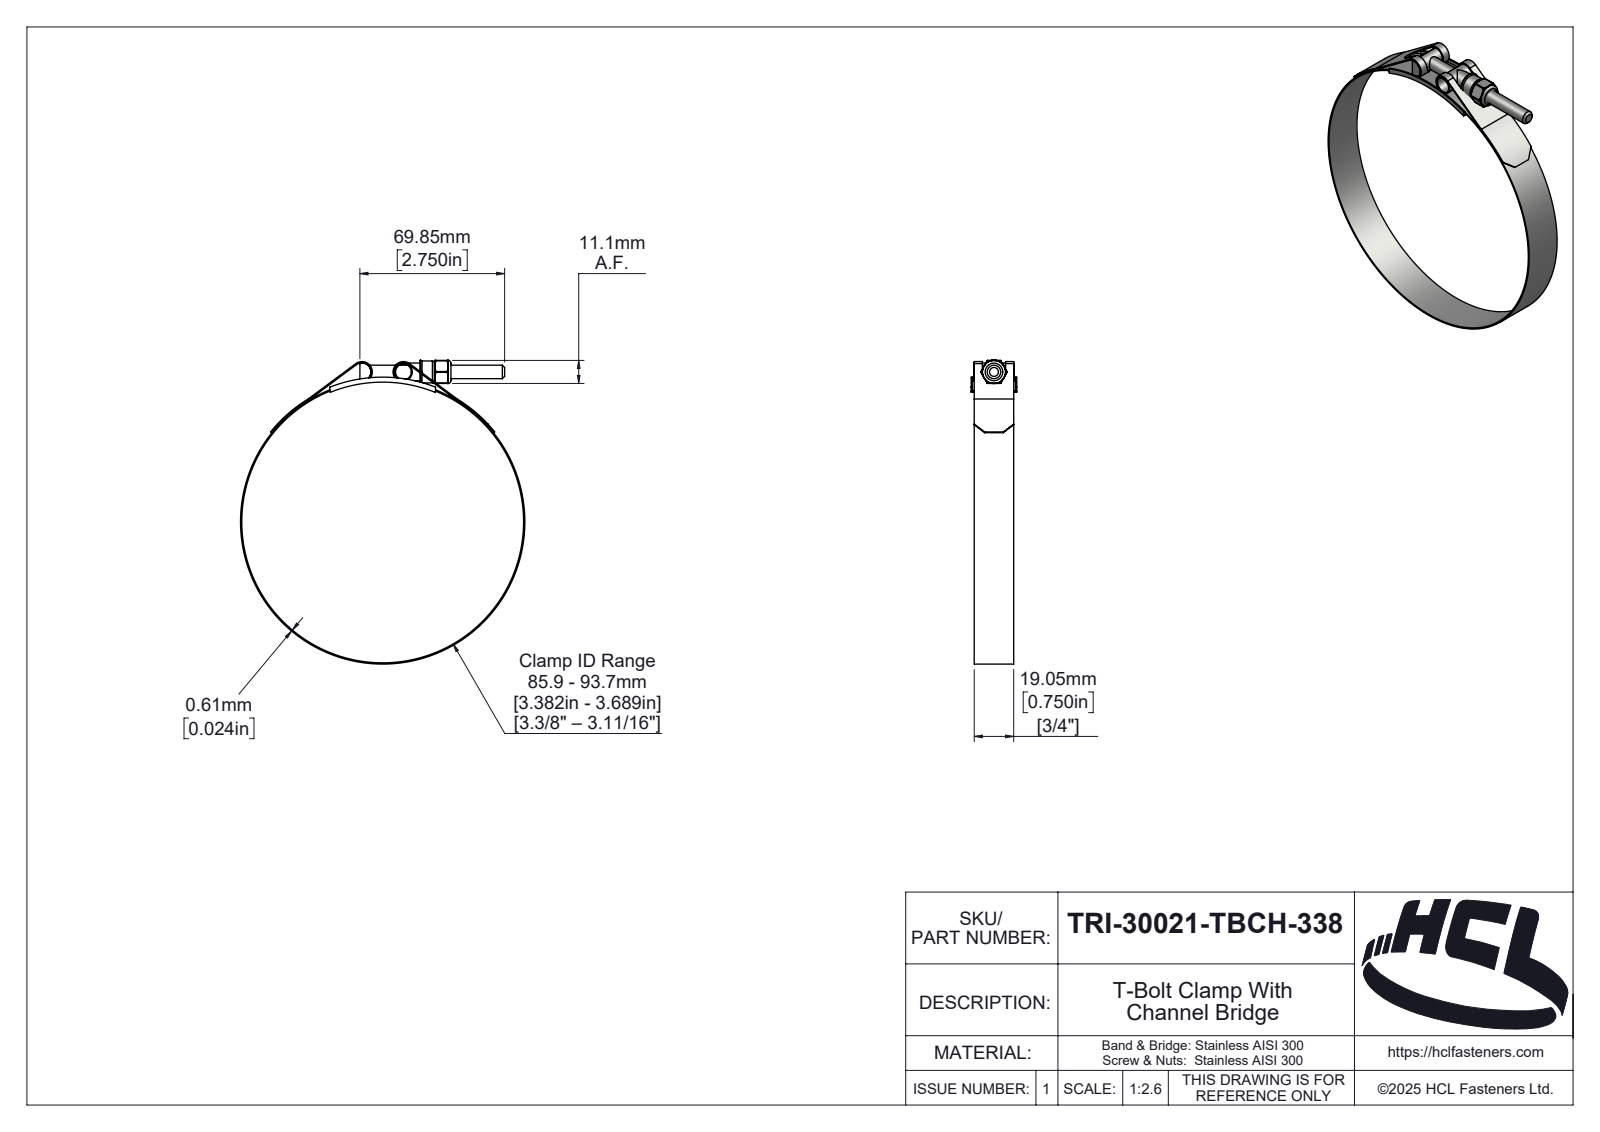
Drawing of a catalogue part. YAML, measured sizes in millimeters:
part_name: "TRI-30021-TBCH-338"
step_written_by: "SolidWorks 2025 (AUTOMOTIVE_DESIGN)"
units: millimeters
bodies: {solids: 6, faces: 330, planar: 46, cylindrical: 122, other: 162}
overall_size: [146.64, 137.22, 22]
volume: 10993
surface_area: 27526
round_holes:
  - {diameter: 5.4, count: 1}
  - {diameter: 6.35, count: 1}
  - {diameter: 6.5, count: 1}
  - {diameter: 7.58, count: 1}
  - {diameter: 136, count: 1}
round_bosses_or_shafts:
  - {diameter: 8.58, count: 2}
  - {diameter: 137.22, count: 1}
  - {diameter: 10.58, count: 1}
partial_cylinders:
  - {radius: 0.39, count: 6}
  - {radius: 0.5, count: 2}
  - {radius: 4.39, count: 2}
  - {radius: 5, count: 2}
  - {radius: 0.59, count: 1}
  - {radius: 2.42, count: 1}
  - {radius: 3.03, count: 1}
  - {radius: 3.19, count: 1}
face_to_face_distances: [0.61, 19.06, 1.47, 20.53, 21.39, 0.86, 19.92, 0.74, 22, 11.11]
hole_center_spacings: [73]
